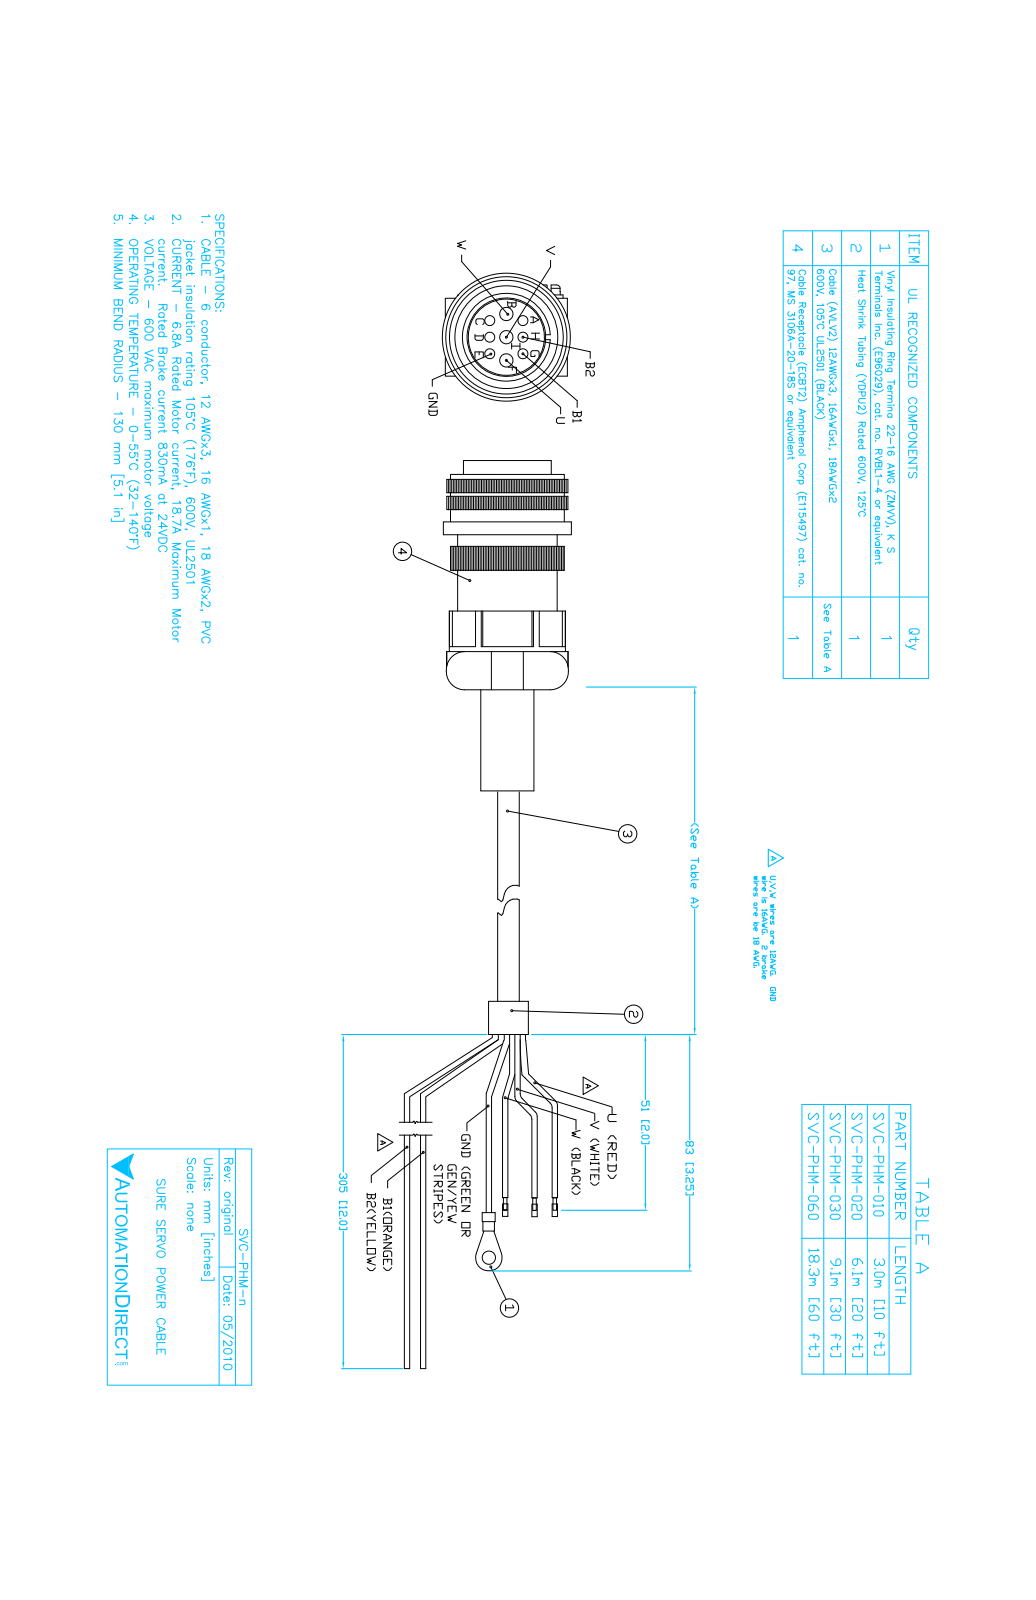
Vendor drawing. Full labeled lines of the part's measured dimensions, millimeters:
Part name (STEP PRODUCT): SVC-PHM-030
STEP written by: SolidWorks 2015 (AUTOMOTIVE_DESIGN)
Units: millimetres
Bodies: 8 solids, 1492 faces (1065 planar, 91 cylindrical, 336 other)
Overall size (bounding box): 169.62 × 68.6 × 37.13
Volume: 81 432 mm³ · Surface area: 39 038 mm²
Round holes (diameter × count): ⌀1.75 ×6, ⌀2.5 ×3, ⌀4 ×2, ⌀15.25 ×1, ⌀16 ×1, ⌀23.7 ×1, ⌀30 ×1, ⌀31 ×1
Round bosses / shafts (diameter × count): ⌀6.5 ×2, ⌀37.13 ×1, ⌀35.3 ×1, ⌀35 ×1, ⌀34.9 ×1, ⌀33.2 ×1, ⌀26.7 ×1, ⌀22.5 ×1
Partial cylindrical surfaces — rounded edges, fillets, slot ends (radius × count): R6.5 ×2, R10.75 ×1, R18.15 ×1
Main face-to-face distances: 4.72, 49.5, 4.7, 10.2, 1.75, 37.55, 39.3, 2.5, 36.8, 47
Hole centre spacings: 8.51, 11.84, 4.37, 5.9, 7.02, 11, 12.18, 5.5
